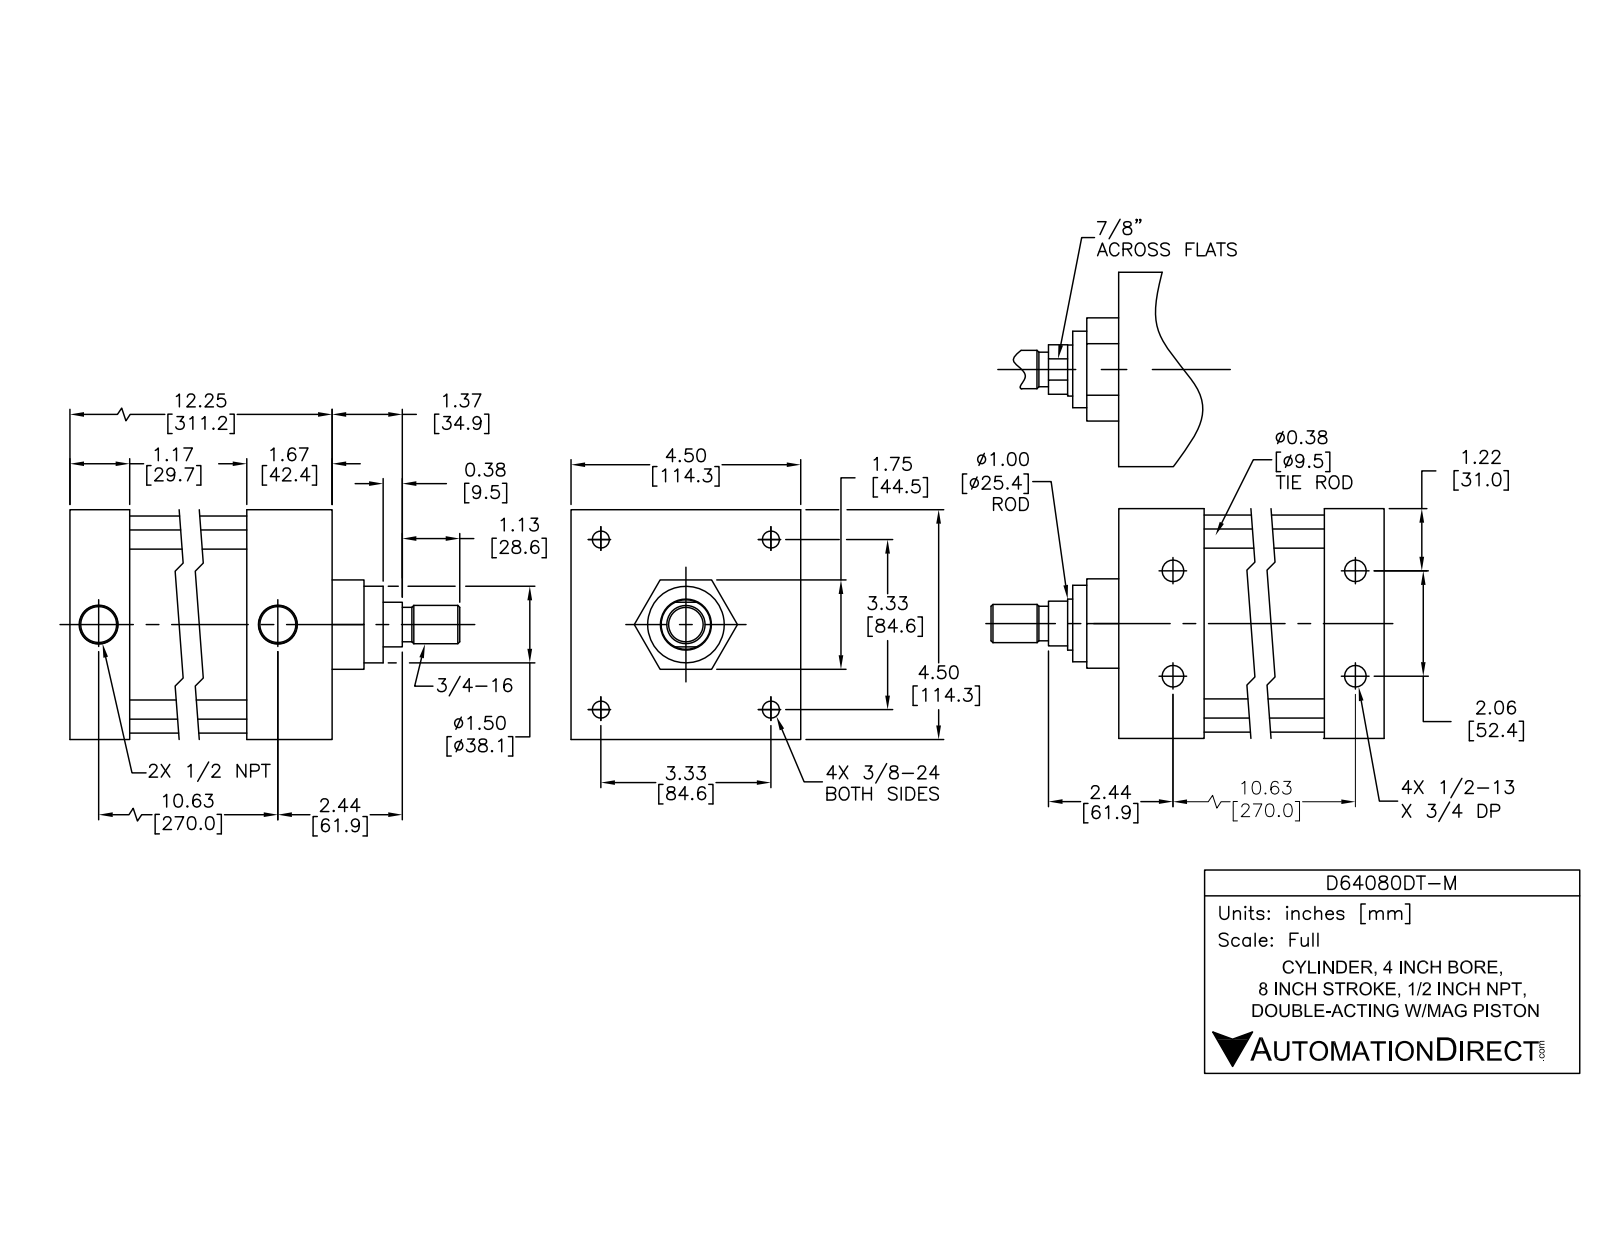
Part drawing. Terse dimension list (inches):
name: D64080DT-M BODY; D64080DT-M PISTON; D64080DT-M
written by: SolidWorks 2015 (AUTOMOTIVE_DESIGN)
unit: in
bodies: 12 solids, 303 faces (99 planar, 114 cylindrical, 90 other)
size: 14.745 × 4.5 × 4.5
volume: 99.45 in³; area: 556.9 in²
holes: 4× ⌀0.33, 4× ⌀0.406, 4× ⌀0.417, 4× ⌀0.625, 2× ⌀0.5, 2× ⌀0.766, 1× ⌀1, 1× ⌀1.003, 1× ⌀4
bosses: 4× ⌀0.609, 4× ⌀0.375, 4× ⌀0.34, 1× ⌀4.25, 1× ⌀3.997, 1× ⌀1.75, 1× ⌀0.997, 1× ⌀0.97
rounds: 4× R0.45
face distances: 4.5, 0.08, 9.326, 12.246, 1.75, 10.997, 1.249, 9.751, 1.246, 2.495
hole spacings: 2.349, 3.322, 10.672, 10.622, 1.031, 1.031, 2.062, 4.698
